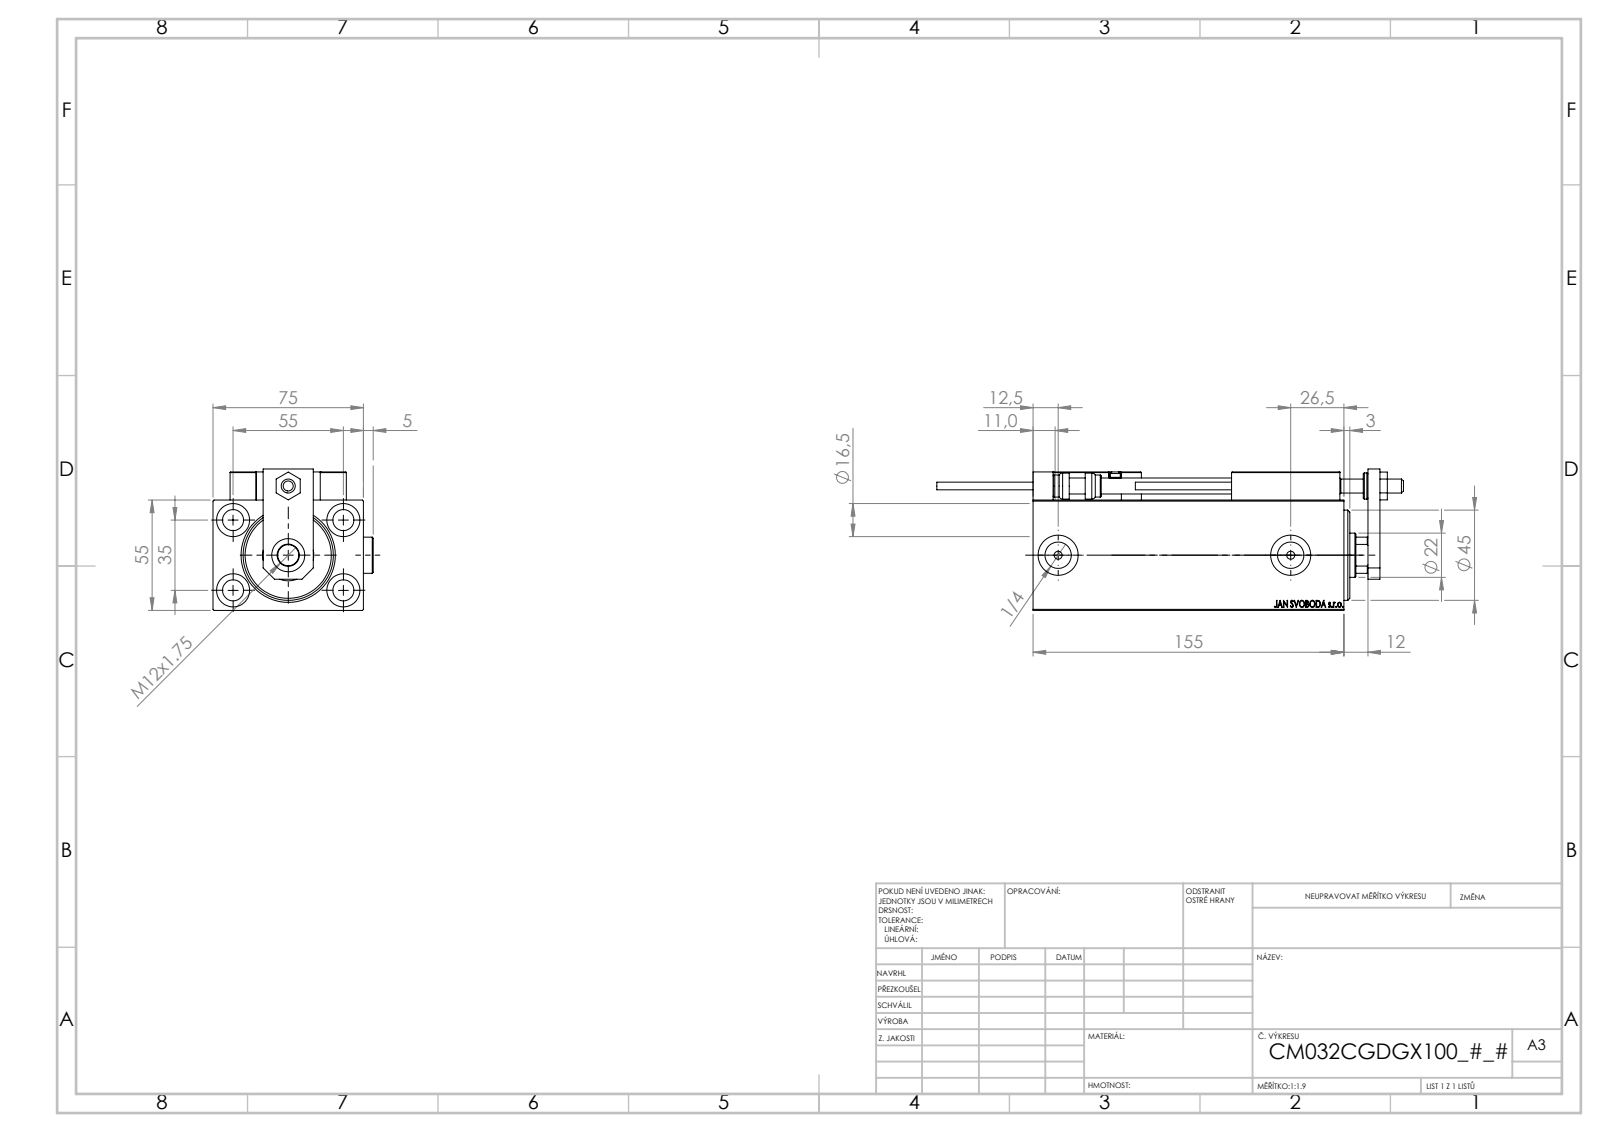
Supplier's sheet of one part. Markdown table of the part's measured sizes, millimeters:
| quantity | value |
| --- | --- |
| part name | SWITCH_X_FRONT_BACK; V450CM_VC_B; ZARAZKA; V450CM_C_Body (+8 more) |
| STEP written by | SolidWorks 2019 (CONFIG_CONTROL_DESIGN) |
| units | millimeters |
| bodies | 25 solids, 1336 faces (594 planar, 204 cylindrical, 538 other) |
| overall size | 232.7 × 79.9 × 70.5 |
| volume | 584 039 mm³ |
| surface area | 134 265 mm² |
| round holes (diameter × count) | 4 × 6, 8 × 5, 10.5 × 5, 16.5 × 5, 3.2 × 4, 5 × 2, 13.16 × 2, 20 × 2, 7 × 1, 22 × 1, 25.5 × 1, 32 × 1 |
| round bosses / shafts (diameter × count) | 18 × 2, 5 × 2, 3.8 × 2, 13 × 1, 11 × 1 |
| partial cylindrical surfaces (radius × count) | 0.3 × 30, 3 × 2, 10.5 × 1 |
| main face-to-face distances | 55, 75, 14, 10, 12, 5, 7, 69, 15, 25 |
| hole center spacings | 32.6, 11.37, 20, 29.59, 29.69, 32.33, 35, 36.06 |
